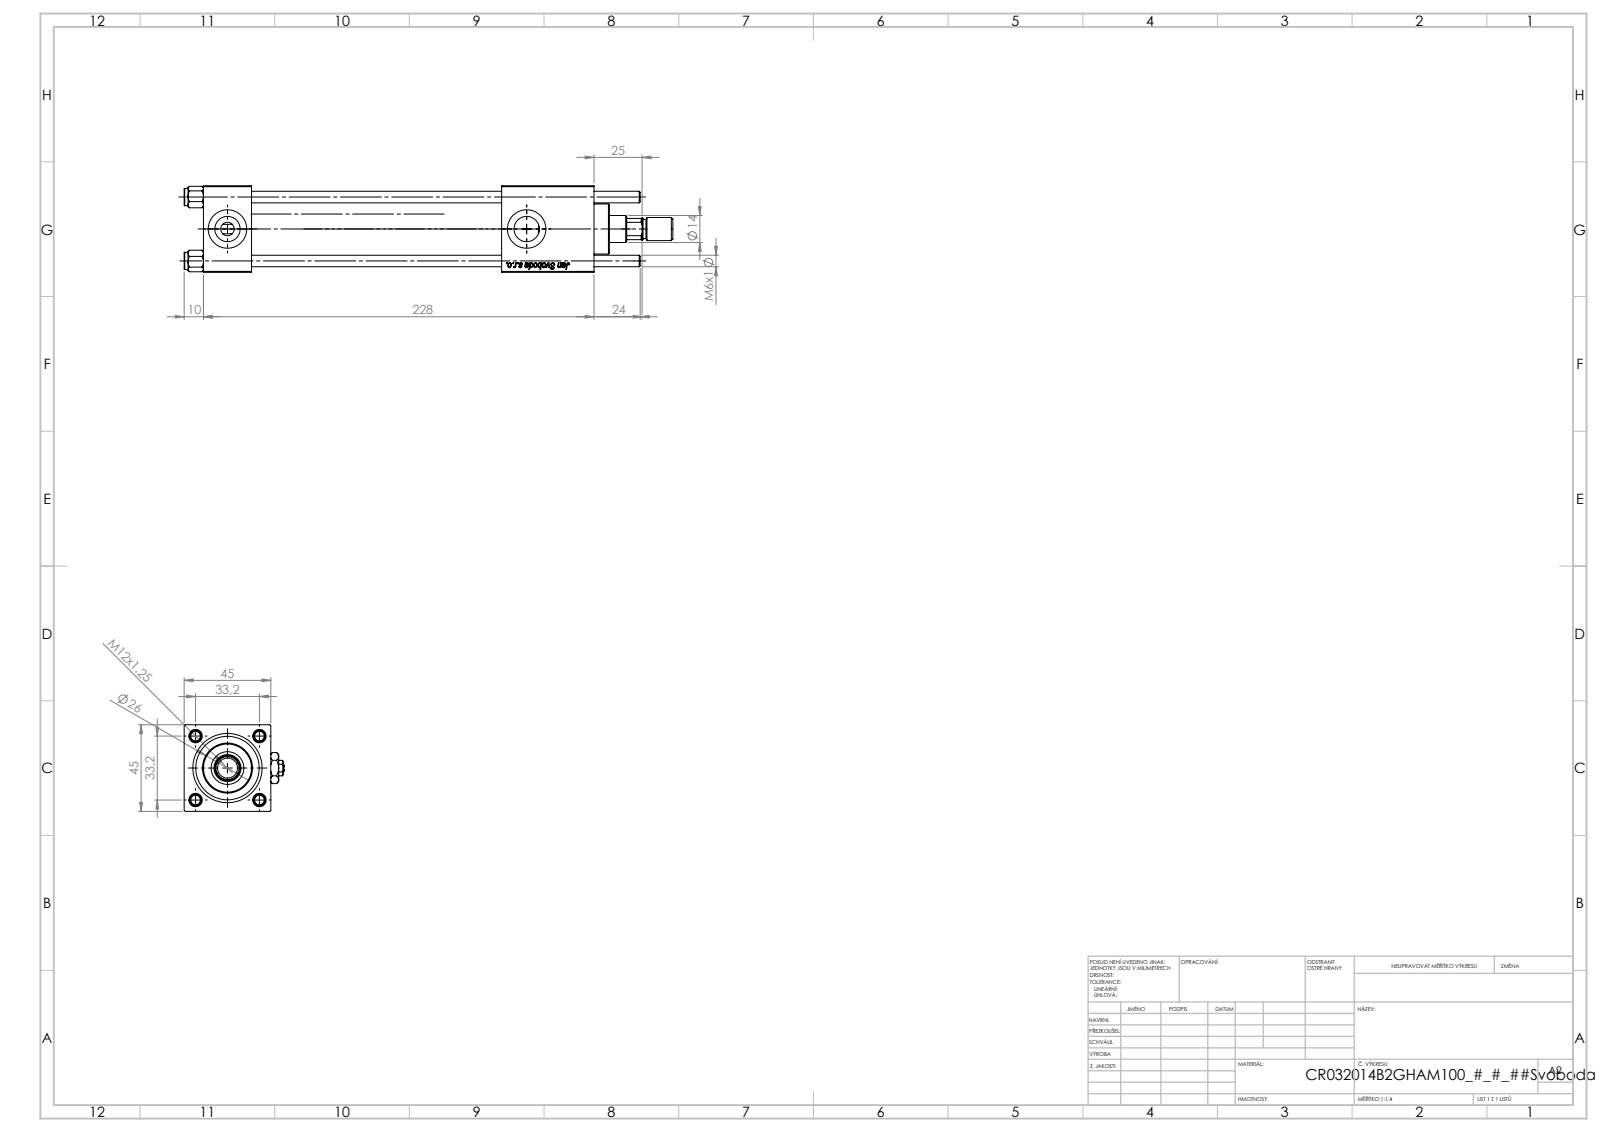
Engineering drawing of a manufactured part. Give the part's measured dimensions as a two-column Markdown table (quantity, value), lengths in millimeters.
| quantity | value |
| --- | --- |
| part name | NUT_M5_B; V215CR_B_TYCINKA; V215CR_B-1; V215_VC_A (+3 more) |
| STEP written by | SolidWorks 2019 (CONFIG_CONTROL_DESIGN) |
| units | millimeters |
| bodies | 13 solids, 1222 faces (458 planar, 88 cylindrical, 676 other) |
| overall size | 254 × 52 × 45 |
| volume | 247 001 mm³ |
| surface area | 101 643 mm² |
| round holes (diameter × count) | 6 × 4, 7 × 2, 13.16 × 2, 20 × 2, 6.5 × 1, 14 × 1, 17 × 1, 24 × 1, 32 × 1, 33 × 1 |
| round bosses / shafts (diameter × count) | 9 × 4, 38 × 1, 26 × 1, 12 × 1, 10 × 1 |
| partial cylindrical surfaces (radius × count) | 6.5 × 1 |
| main face-to-face distances | 45, 25, 203, 178, 155, 130, 48, 174.3, 149.3, 19.3 |
| hole center spacings | 23.48, 33.2, 46.95, 155.5 |
